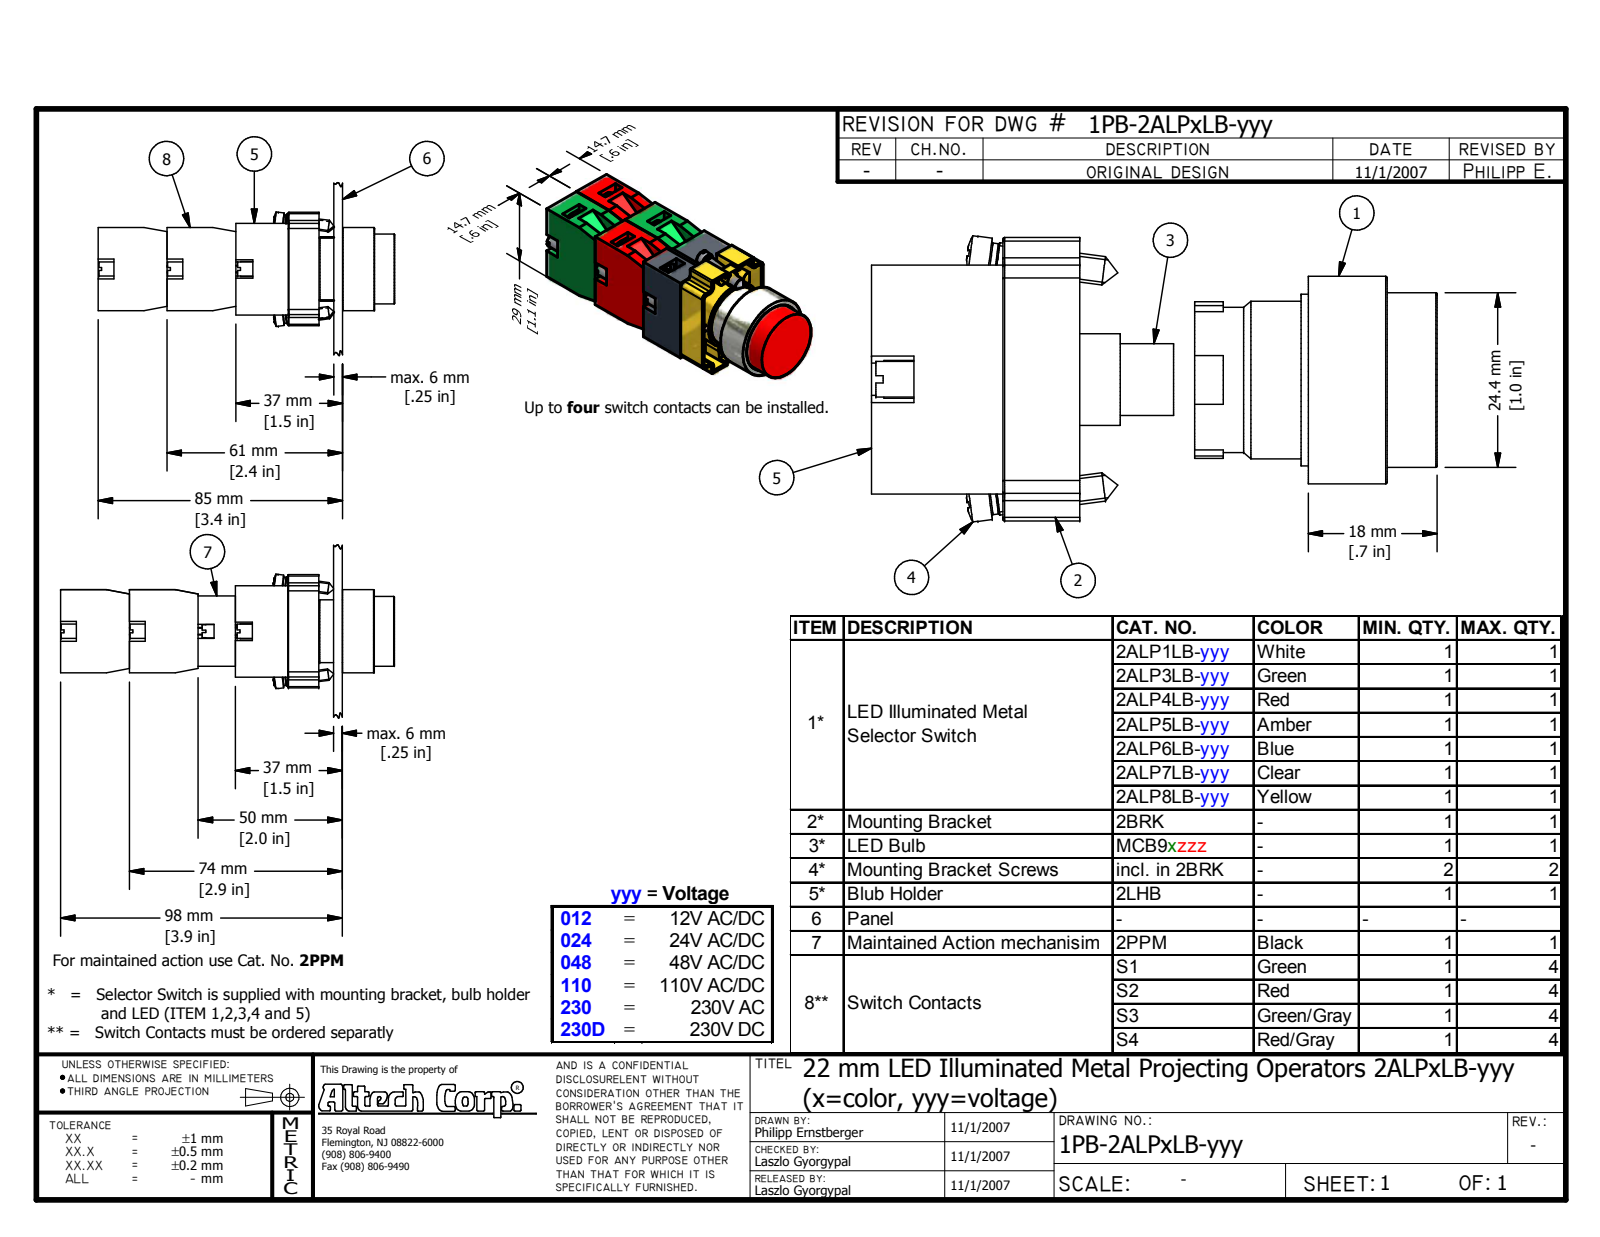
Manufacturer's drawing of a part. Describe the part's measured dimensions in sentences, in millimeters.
The part is named "2ALPxLB-yyy_assembly; 2BRK; DIN 7985 (Z) M4x18-Z; S1 (+8 more)". Its 3-D file was written by "Autodesk Inventor 2008 (AUTOMOTIVE_DESIGN)". It is 28 solids with 1085 faces: 587 planar, 179 cylindrical and 319 other. Overall it measures 103.4 by 60.45 by 45 millimeters. Its volume is 71 608 cubic millimeters and its surface area 46 558 square millimeters. Round holes: 5 of diameter 2.5, 2 of diameter 2.6, 1 of diameter 13.3, 1 of diameter 18, 1 of diameter 22, 1 of diameter 22.25, 1 of diameter 22.5, 1 of diameter 25, 1 of diameter 27. Round bosses or shafts: 8 of diameter 3, 6 of diameter 2.75, 4 of diameter 5, 4 of diameter 1.5, 2 of diameter 4, 2 of diameter 3.65, 1 of diameter 29, 1 of diameter 24.4. Partial cylindrical surfaces (rounded edges, fillets, slot ends): 14 of radius 1, 10 of radius 0.25, 8 of radius 0.72, 5 of radius 2.25, 4 of radius 0.5, 4 of radius 0.8, 4 of radius 1.8, 4 of radius 2. The main face-to-face distances are 14.8, 14.7, 3, 24, 14.95, 15.05, 29.75, 15.91, 18.91, 29.5. The hole center spacings are 14.53, 6.52, 6.57, 13, 25.88, 26, 26.27, 29.07.
